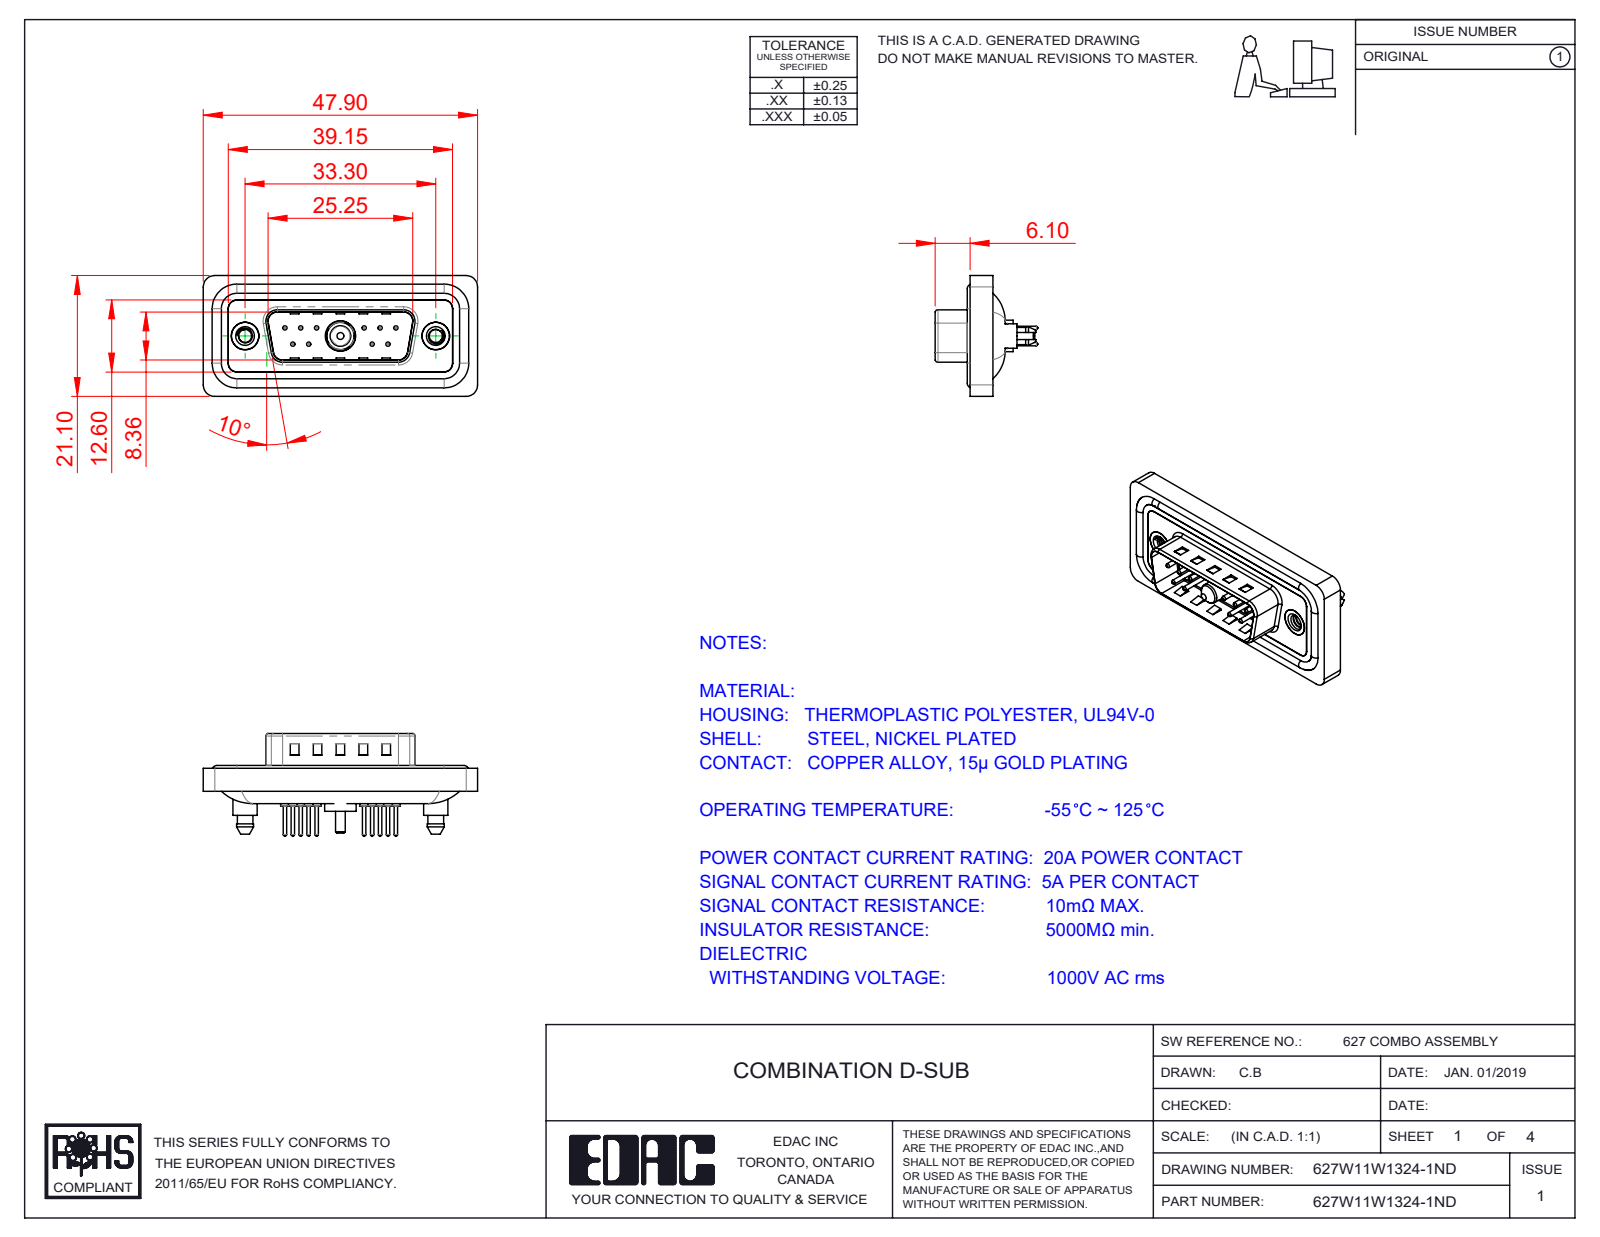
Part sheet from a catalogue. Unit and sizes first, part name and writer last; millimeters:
Units: millimetres
Overall size (bounding box): 47.9 × 21.1 × 17.9
Round holes (diameter × count): ⌀0.75 ×10, ⌀1.6 ×10, ⌀2 ×10, ⌀2.26 ×2, ⌀4 ×2, ⌀4.8 ×2, ⌀5 ×2, ⌀4.85 ×1, ⌀5.3 ×1
Round bosses / shafts (diameter × count): ⌀1.5 ×10, ⌀0.6 ×10, ⌀1.6 ×4, ⌀5.4 ×2, ⌀4.9 ×2, ⌀4.25 ×2, ⌀5.5 ×1, ⌀5.2 ×1
Partial cylindrical surfaces — rounded edges, fillets, slot ends (radius × count): R1.5 ×28, R2 ×20, R1.6 ×10, R0.5 ×8, R1 ×7, R0.25 ×4, R0.6 ×4, R0.65 ×4
Main face-to-face distances: 0.4, 1.1, 1.6, 1.5, 2.9, 0.5, 3.1, 4.1, 0.82, 9.58
Hole centre spacings: 3.16, 2.77, 13.85, 11.08, 16.62, 5.03, 5.04, 5.54
Volume: 5 568 mm³ · Surface area: 9 160 mm²
Bodies: 19 solids, 927 faces (282 planar, 387 cylindrical, 258 other)
Part name (STEP PRODUCT): 627Combo Shell Rear_15 Contacts; 627Combo Shell Front_15 Contacts; Power Pin_10A S; 627Combo Housing_11W1 (+6 more)
STEP written by: SolidWorks 2023 (CONFIG_CONTROL_DESIGN)
